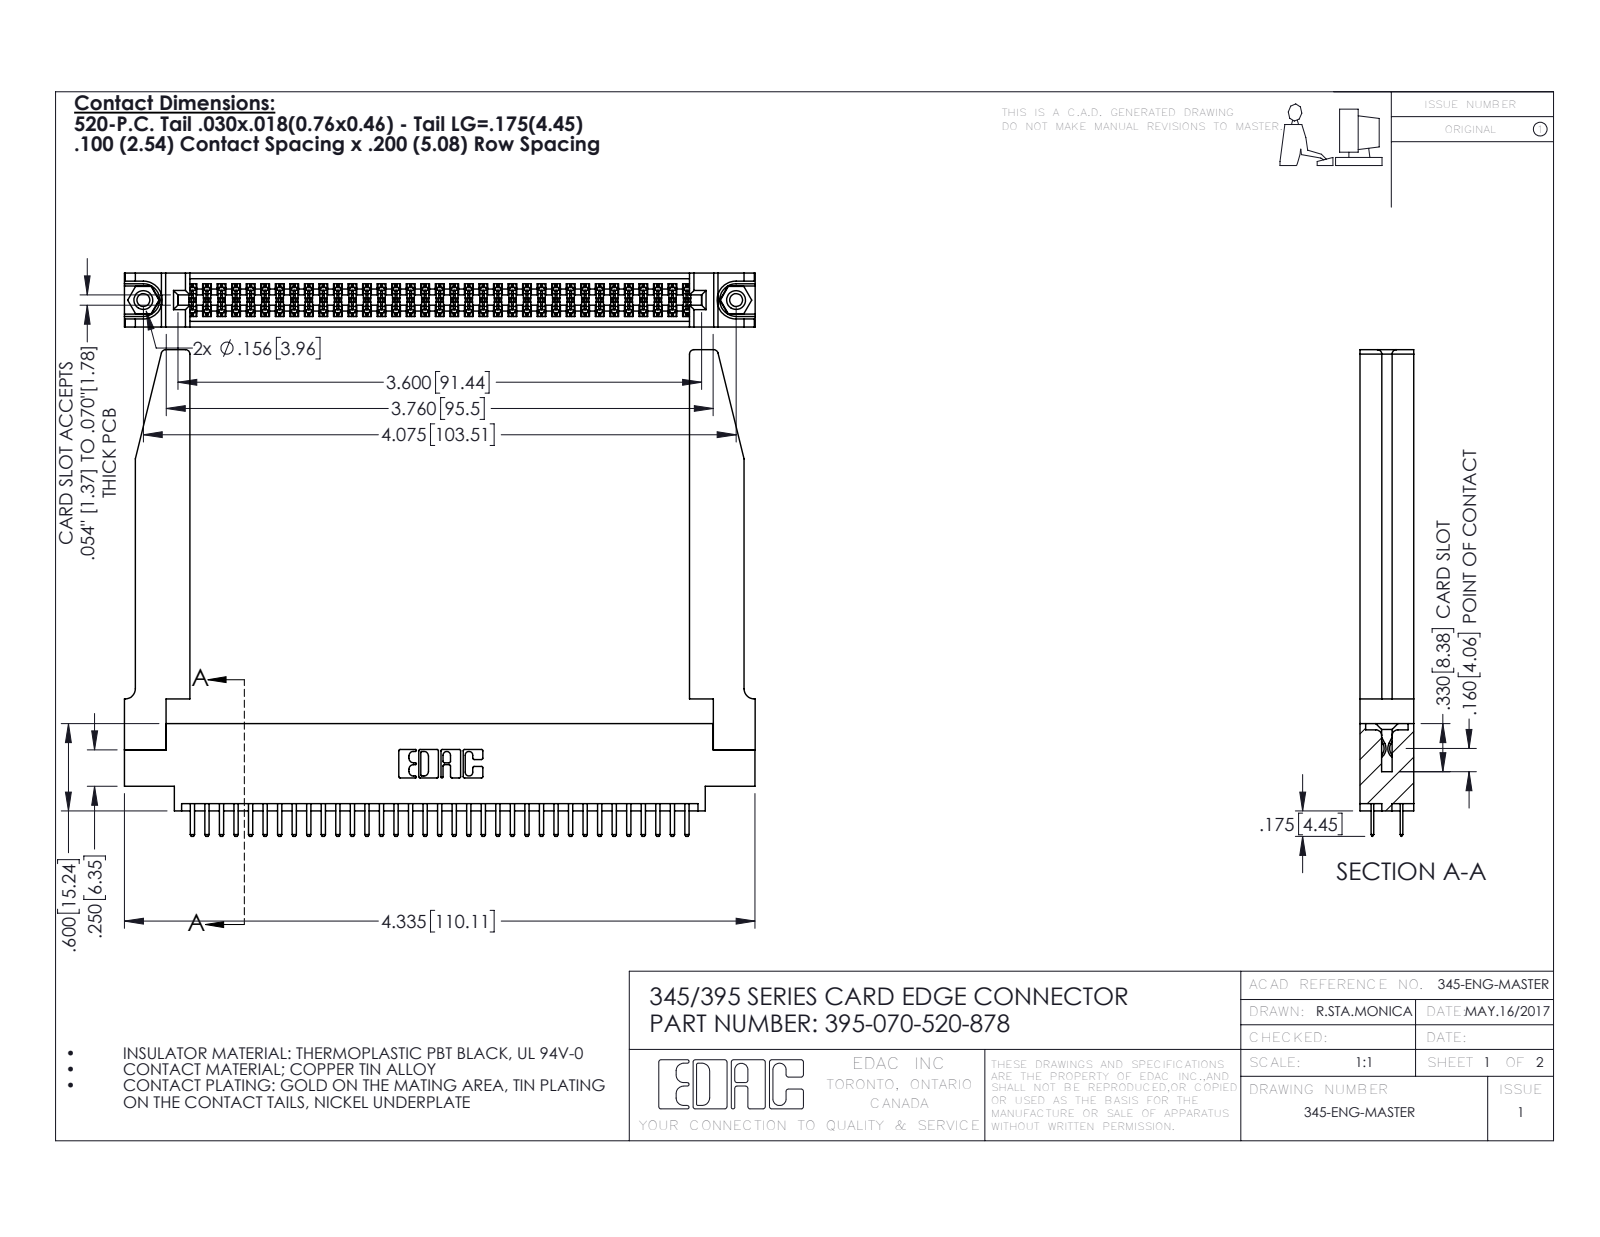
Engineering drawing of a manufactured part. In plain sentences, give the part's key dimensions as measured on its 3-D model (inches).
The part is named "345-292-001_345-293-120; 395-070-520-878; 345-250-001_345-250-001-102; 345-220-078_345-220-078 (+1 more)". Its 3-D file was written by "SolidWorks 2016 (CONFIG_CONTROL_DESIGN)". It is 75 solids with 4144 faces: 2676 planar, 1416 cylindrical and 52 other. Overall it measures 4.336 by 3.345 by 0.37 inches. Its volume is 1.114 cubic inches and its surface area 34.54 square inches. Round holes: 2 of diameter 0.089, 2 of diameter 0.125, 2 of diameter 0.156, 1 of diameter 0.064. Round bosses or shafts: 2 of diameter 0.155. Partial cylindrical surfaces (rounded edges, fillets, slot ends): 105 of radius 0.006, 74 of radius 0.01, 22 of radius 0.01, 8 of radius 0.03, 6 of radius 0.007, 6 of radius 0.031, 3 of radius 0.026, 2 of radius 0.014. The main face-to-face distances are 0.37, 0.072, 0.298, 0.2, 0.098, 0.272, 0.025, 0.225, 0.022, 0.175. The hole center spacings are 0.27, 3.839, 4.075.
